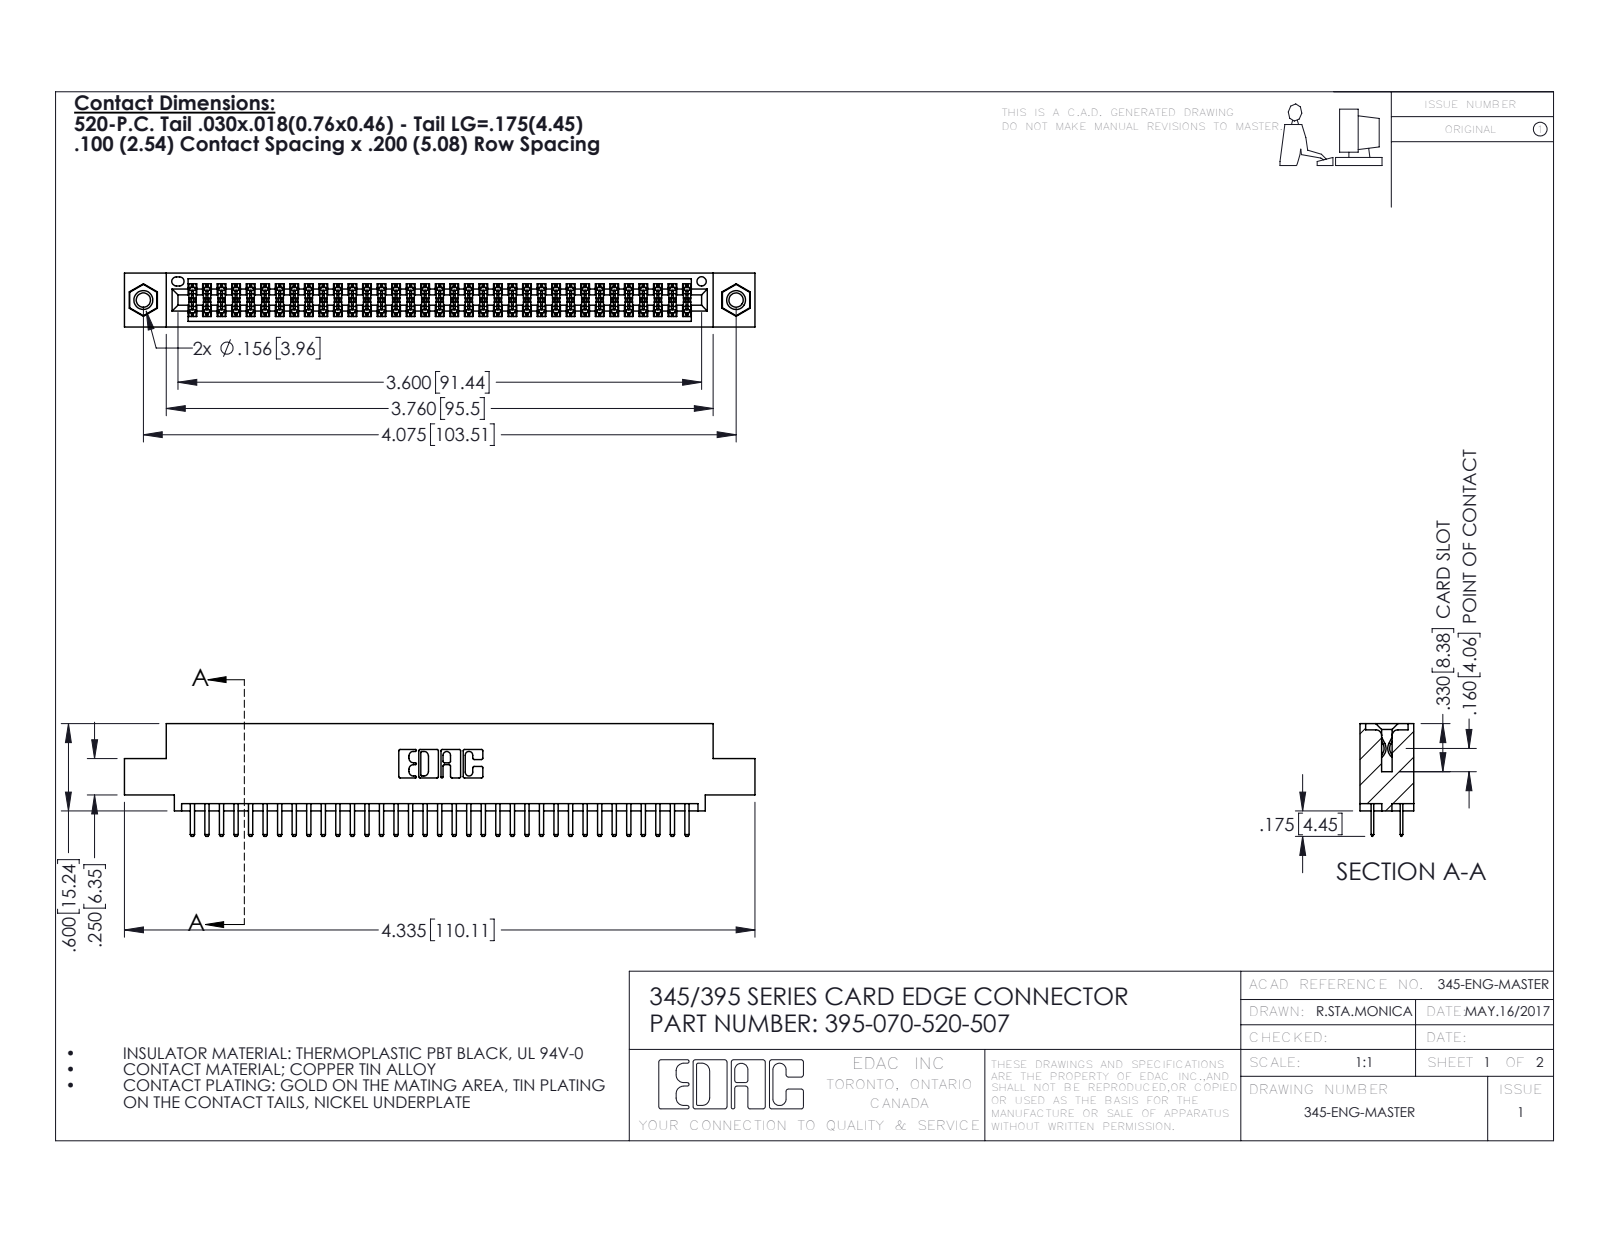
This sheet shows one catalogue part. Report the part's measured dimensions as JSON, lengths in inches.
{"part_name": "345-292-001_345-293-120; 345-250-001_345-250-005-103; 345 Part_0.110 Offset - 0.156 Dia-TI; 395-070-520-507", "step_written_by": "SolidWorks 2016 (CONFIG_CONTROL_DESIGN)", "units": "inches", "bodies": {"solids": 73, "faces": 3970, "planar": 2566, "cylindrical": 1388, "other": 16}, "overall_size": [4.335, 0.775, 0.37], "volume_in3": 0.642, "surface_area_in2": 23.96, "round_holes": [[0.098, 2], [0.125, 2], [0.156, 2], [0.064, 1]], "round_bosses_or_shafts": [[0.155, 2]], "partial_cylinders_radius": [[0.006, 105], [0.01, 74], [0.01, 22], [0.007, 6], [0.031, 6], [0.026, 3], [0.014, 2], [0.019, 2]], "face_to_face_distances": [0.072, 0.298, 0.2, 0.37, 0.098, 0.272, 0.025, 0.225, 0.022, 0.072], "hole_center_spacings": [0.27, 3.839, 4.075]}
